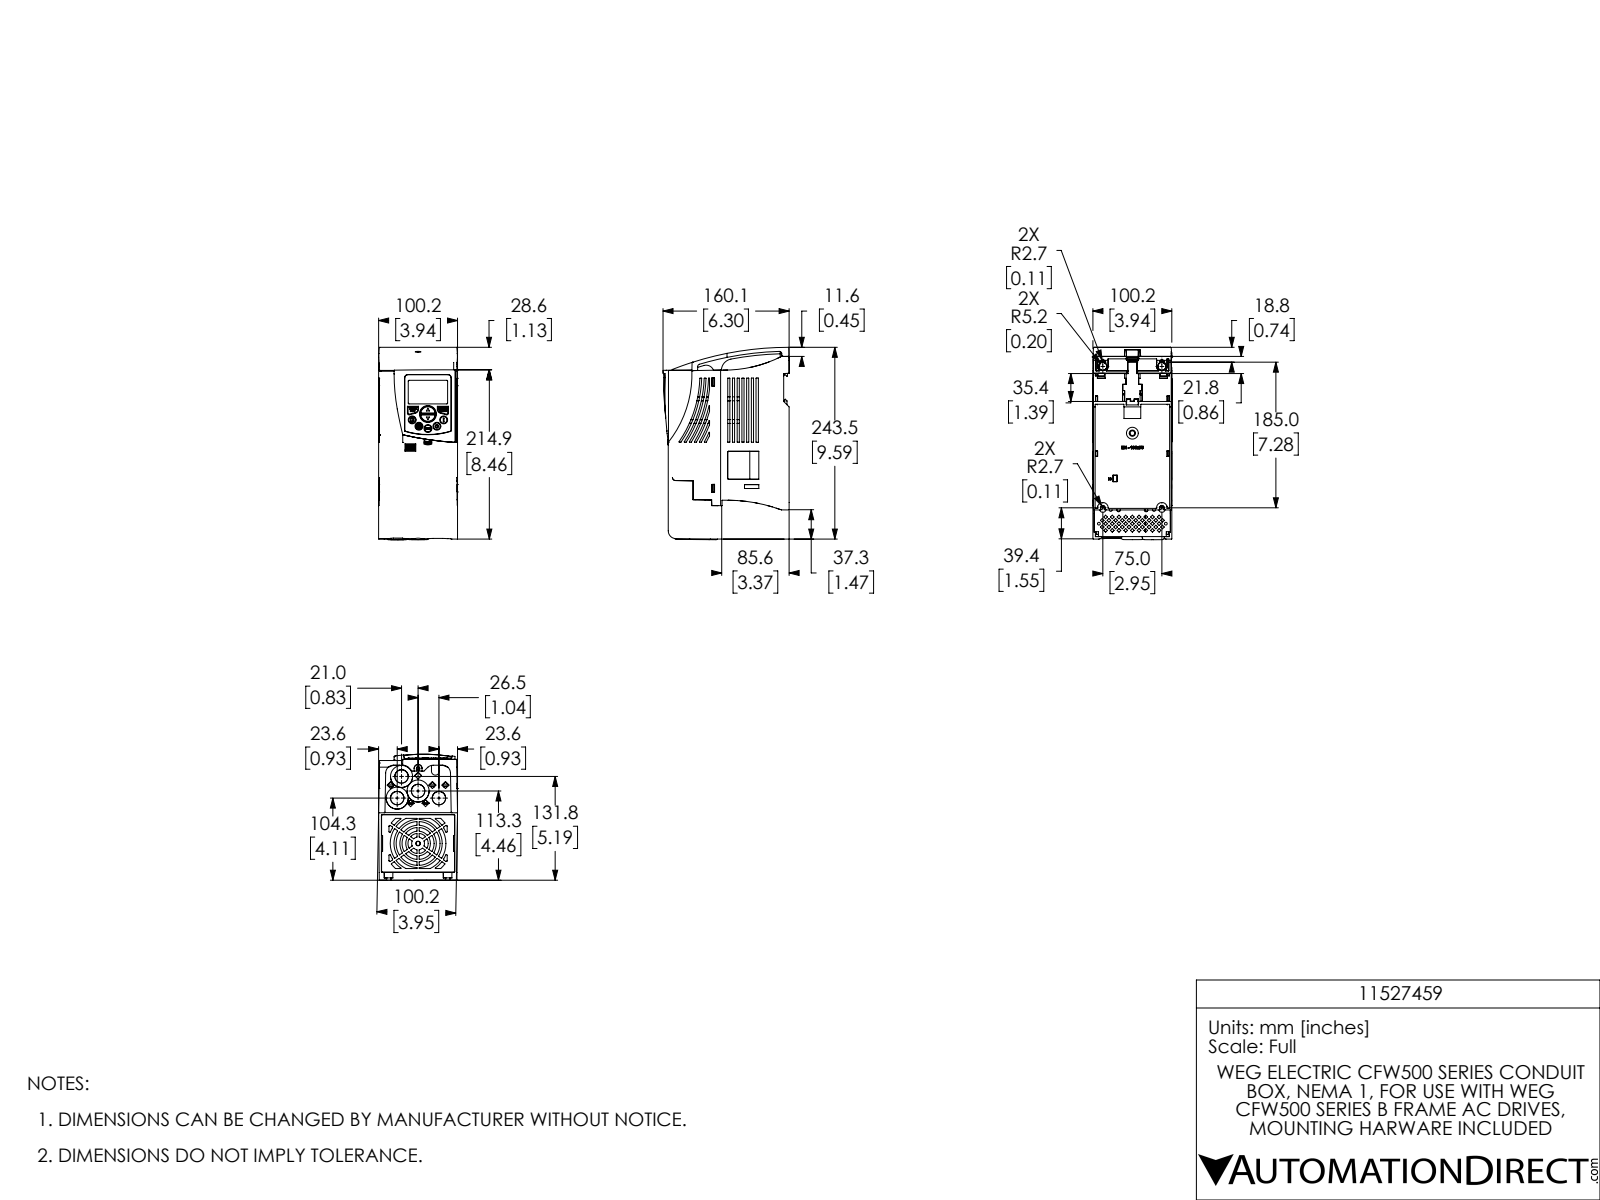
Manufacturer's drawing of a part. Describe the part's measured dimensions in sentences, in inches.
The part is named "CFW50X_FRAME_B_NEMA1_PAR fStep r2b red1b ext3C b3 NC minor redonly 2 r1b covr". Its 3-D file was written by "SolidWorks 2017 (AUTOMOTIVE_DESIGN)". It is 25 solids with 4644 faces: 2001 planar, 989 cylindrical and 1654 other. Overall it measures 9.62 by 6.304 by 3.946 inches. Its volume is 150.5 cubic inches and its surface area 388.8 square inches. Round holes: 7 of diameter 0.138, 4 of diameter 0.669, 4 of diameter 0.886, 2 of diameter 0.165, 2 of diameter 0.177, 1 of diameter 0.846. Round bosses or shafts: 5 of diameter 0.394, 4 of diameter 1.102, 4 of diameter 1.024, 2 of diameter 0.886, 2 of diameter 0.386, 1 of diameter 0.787. Partial cylindrical surfaces (rounded edges, fillets, slot ends): 348 of radius 0.012, 88 of radius 0.008, 41 of radius 0.01, 36 of radius 0.02, 20 of radius 0.039, 8 of radius 0.098, 6 of radius 0.079, 6 of radius 0.157. The main face-to-face distances are 0.122, 5.65, 0.05, 0.102, 5.772, 0.123, 0.073, 0.059, 5.713, 0.063. The hole center spacings are 1.102, 0.394, 1.772, 1.102, 0.393, 0.395, 0.903, 1.198.
